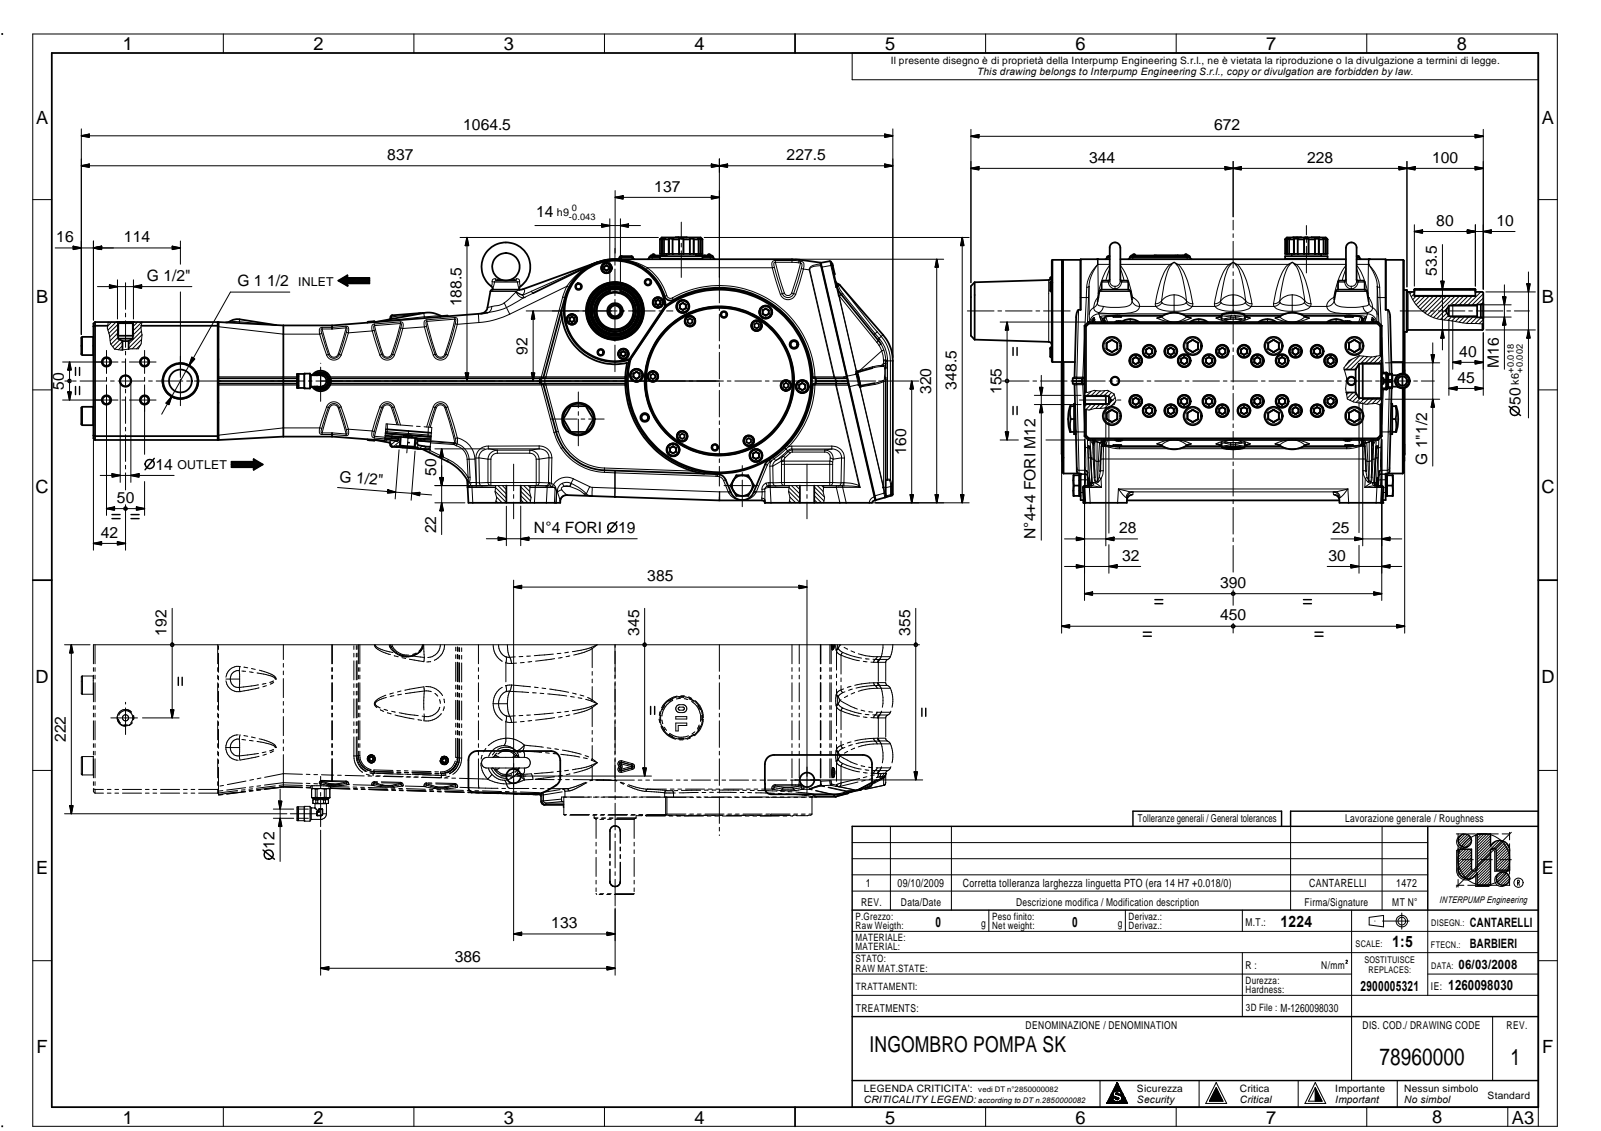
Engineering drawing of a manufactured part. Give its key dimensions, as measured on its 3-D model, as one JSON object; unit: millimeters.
{"step_written_by": "THINKDESIGN (CONFIG_CONTROL_DESIGN)", "units": "millimeters", "bodies": {"solids": 128, "faces": 8858, "planar": 1857, "cylindrical": 2731, "other": 4270}, "overall_size": [1064.49, 672, 348.8], "volume_mm3": 81640000, "surface_area_mm2": 4150000, "round_holes": [[17, 34], [8.5, 32], [10.5, 30], [13.5, 21], [6.75, 17], [5, 14], [16.5, 14], [14, 13], [19, 7], [7, 6], [8, 5], [2.25, 4]], "round_bosses_or_shafts": [[16, 38], [10, 38], [13, 24], [8, 21], [6, 8], [24, 6], [2.1, 4], [60.1, 2]], "partial_cylinders_radius": [[0.5, 819], [2, 226], [4, 156], [1.5, 103], [3, 50], [12, 45], [1, 28], [2.5, 25]], "face_to_face_distances": [237.5, 82.5, 25.1, 5, 10, 317, 79.5, 85, 155, 234.5], "hole_center_spacings": [168, 168.03, 336, 377.77, 109, 341.22, 446.46, 338.61]}
